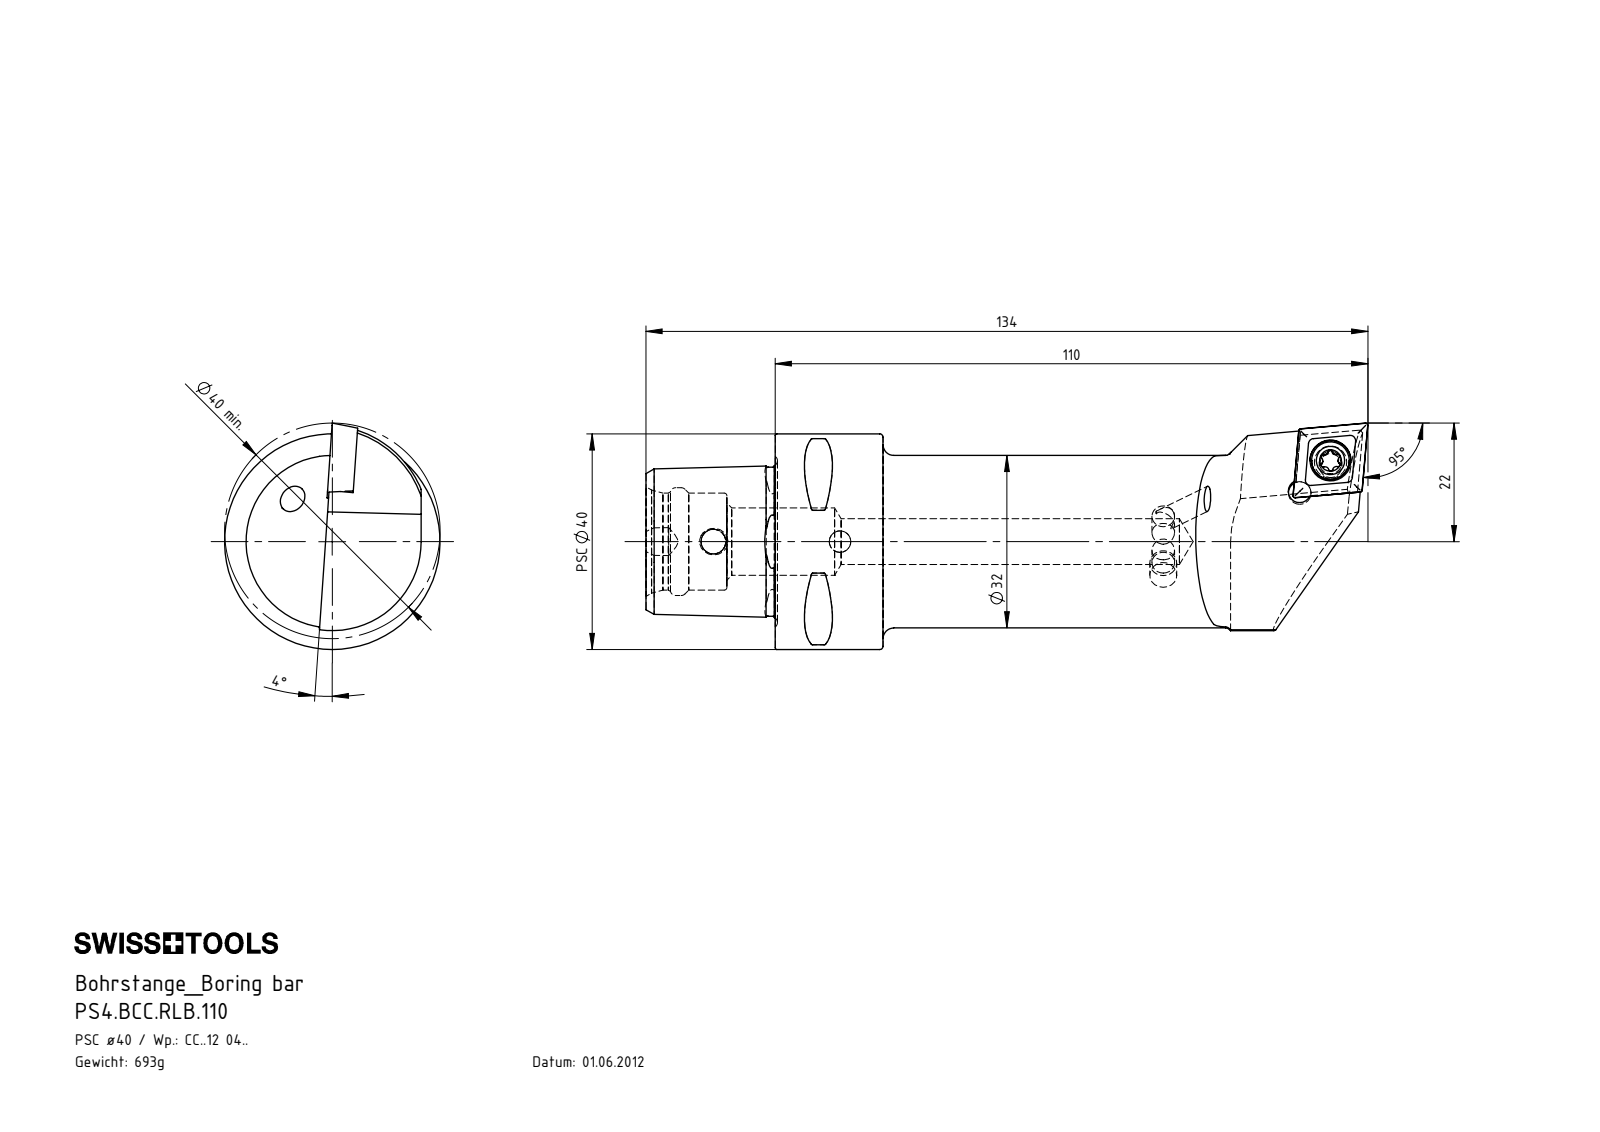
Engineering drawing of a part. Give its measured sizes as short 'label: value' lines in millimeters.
name: PS4.BCC.RLB.110; CCMT120404; PS4-BCC.RLB.110_A; WCC-ER2.001.010_A (+1 more)
written by: SolidWorks 2017 (AUTOMOTIVE_DESIGN)
unit: mm
bodies: 5 solids, 288 faces (49 planar, 73 cylindrical, 166 other)
size: 134 × 42 × 40
volume: 87 001 mm³; area: 20 001 mm²
holes: 4× ⌀4.2, 2× ⌀4, 1× ⌀4.6, 1× ⌀5, 1× ⌀5.5, 1× ⌀7.6, 1× ⌀8.5, 1× ⌀12.5, 1× ⌀18, 1× ⌀20
bosses: 2× ⌀5, 1× ⌀40, 1× ⌀32, 1× ⌀7
rounds: 8× R0.3, 6× R0.39, 3× R0.69, 3× R0.69, 2× R3, 1× R16.5, 1× R19
face distances: 4.45, 20, 24, 44, 15.52, 35.3, 15, 9, 29, 4.76
hole spacings: 8.09, 23.5
